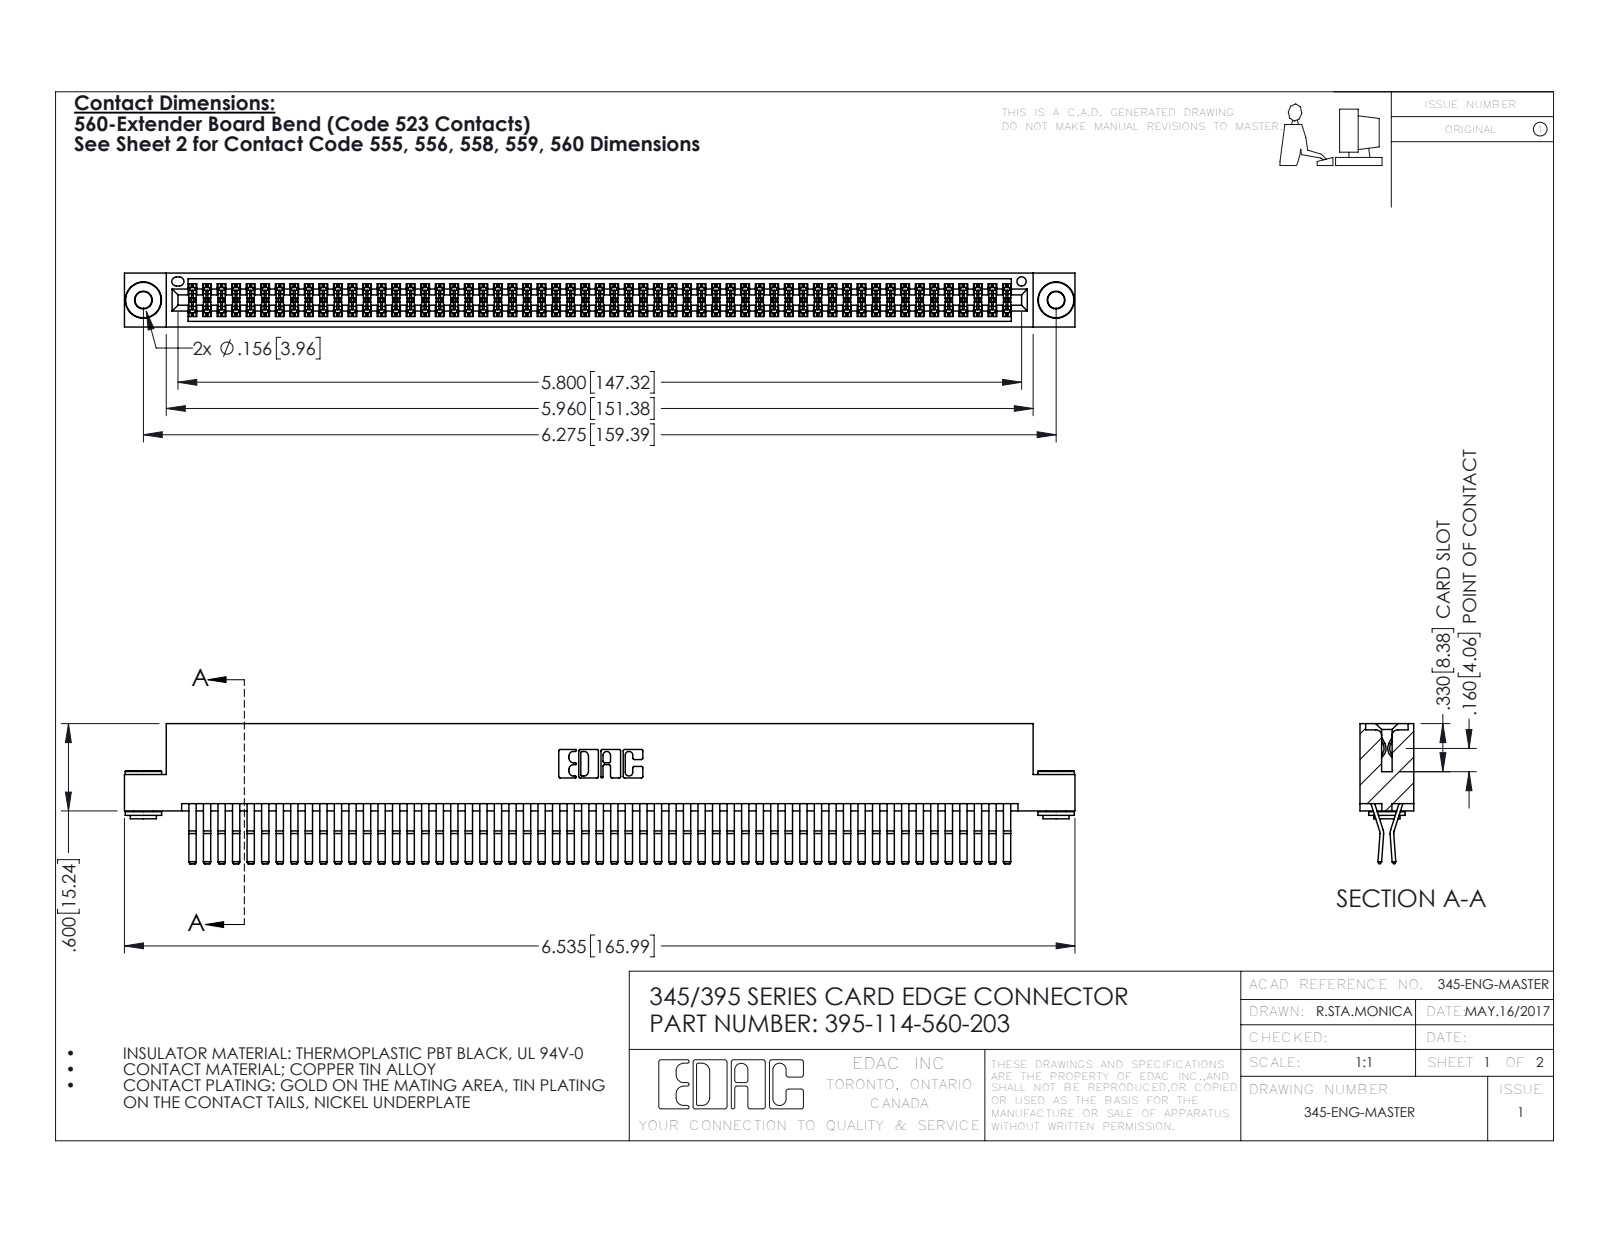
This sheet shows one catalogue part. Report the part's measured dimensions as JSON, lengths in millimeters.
{"part_name": "345 Part_Flush Mounting Lugs - 0.156 Dia-TH; 395-114-560-203; 345-292-001_560 Tail; 345-250-002_345-250-002-102", "step_written_by": "SolidWorks 2016 (CONFIG_CONTROL_DESIGN)", "units": "millimeters", "bodies": {"solids": 117, "faces": 6092, "planar": 3852, "cylindrical": 2232, "other": 8}, "overall_size": [166, 24.4, 9.4], "volume_mm3": 17030, "surface_area_mm2": 27590, "round_holes": [[2.9, 2], [4, 2], [1.6, 1]], "round_bosses_or_shafts": [[6.4, 2], [4.6, 2], [3.5, 2]], "partial_cylinders_radius": [[0.2, 171], [0.3, 22], [0.2, 6], [0.8, 6], [0.7, 3], [0.3, 2], [0.4, 2], [0.5, 2]], "face_to_face_distances": [0.6, 1.8, 7.6, 9.4, 5.1, 2.5, 6.9, 5.7, 4.4, 3.8], "hole_center_spacings": [6.9, 153.4, 159.4]}
